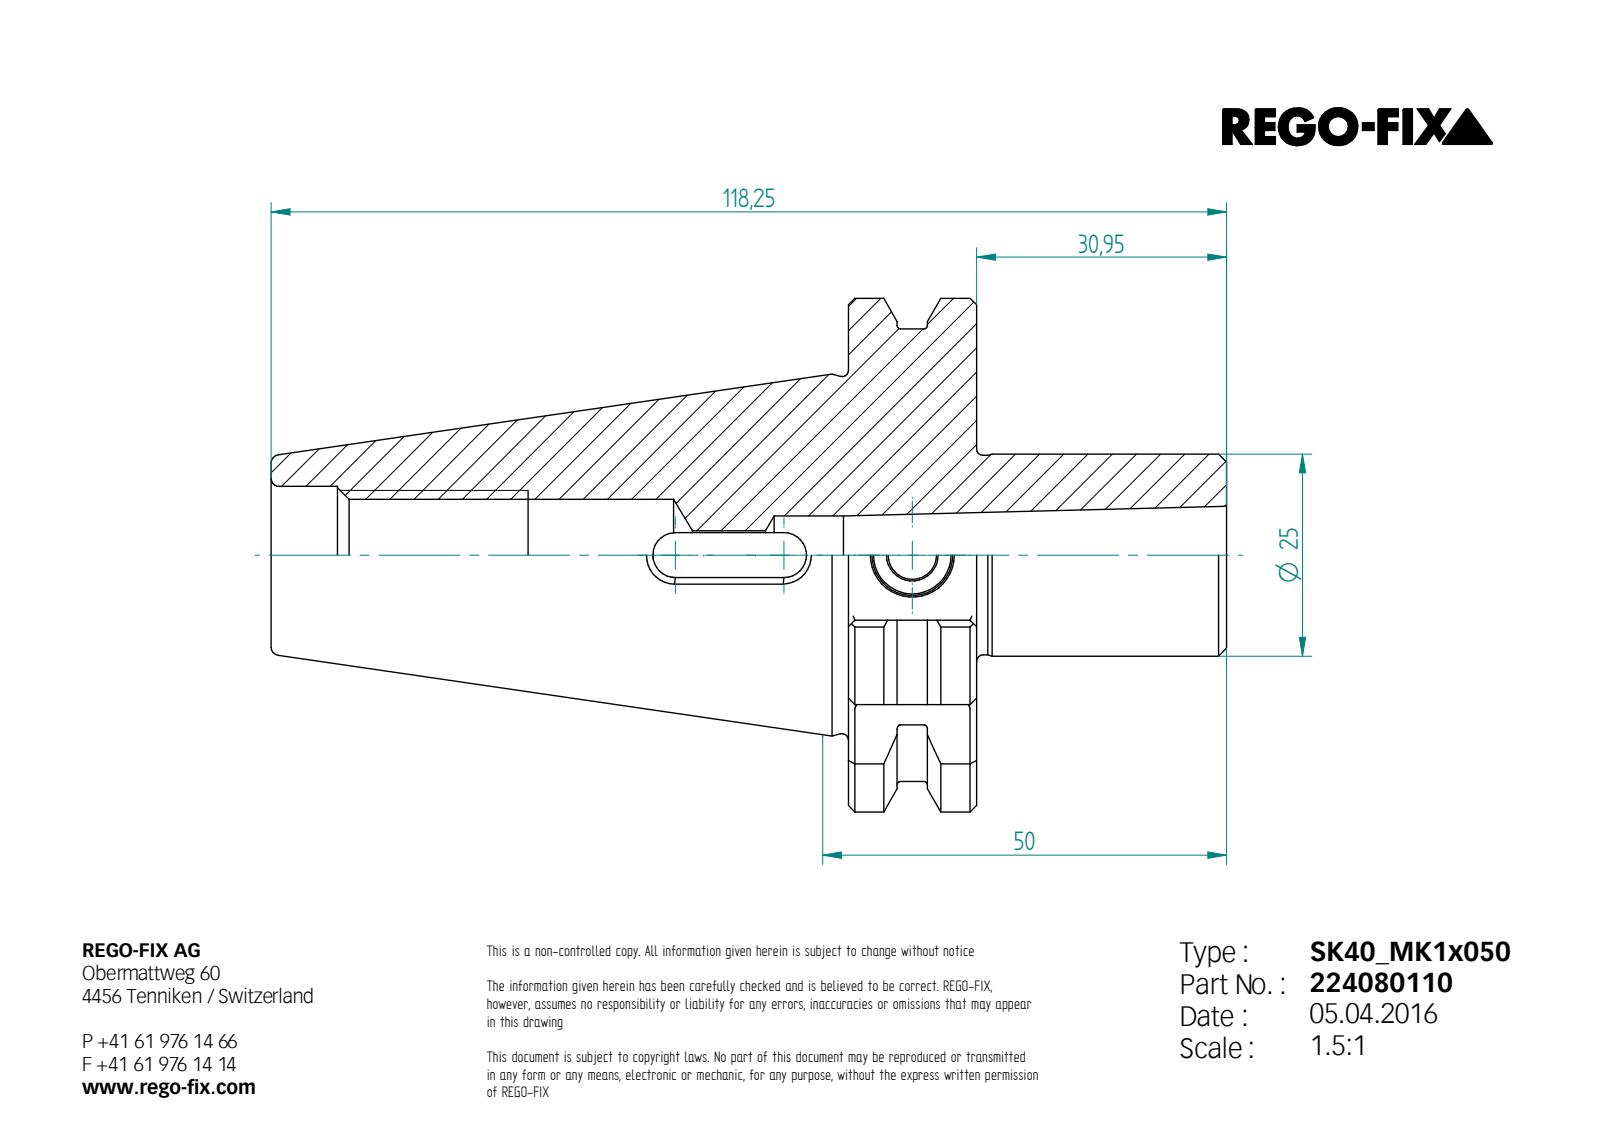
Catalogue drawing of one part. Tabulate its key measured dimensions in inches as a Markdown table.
| quantity | value |
| --- | --- |
| STEP written by | Unknown (AUTOMOTIVE_DESIGN) |
| units | inches |
| bodies | 1 solid, 125 faces (44 planar, 36 cylindrical, 45 other) |
| overall size | 4.656 × 2.502 × 2.402 |
| volume | 6.774 in³ |
| surface area | 37.6 in² |
| round holes (diameter × count) | 0.236 × 1, 0.382 × 1, 0.394 × 1, 0.545 × 1, 0.669 × 1 |
| round bosses / shafts (diameter × count) | 0.984 × 1, 0.972 × 1 |
| partial cylindrical surfaces (radius × count) | 0.02 × 13, 0.109 × 2, 0.118 × 1, 1.102 × 1, 1.251 × 1 |
| main face-to-face distances | 0.624, 0.218, 1.843, 1.219, 0.208, 0.426, 1.862, 0.634, 2.813, 3.437 |
